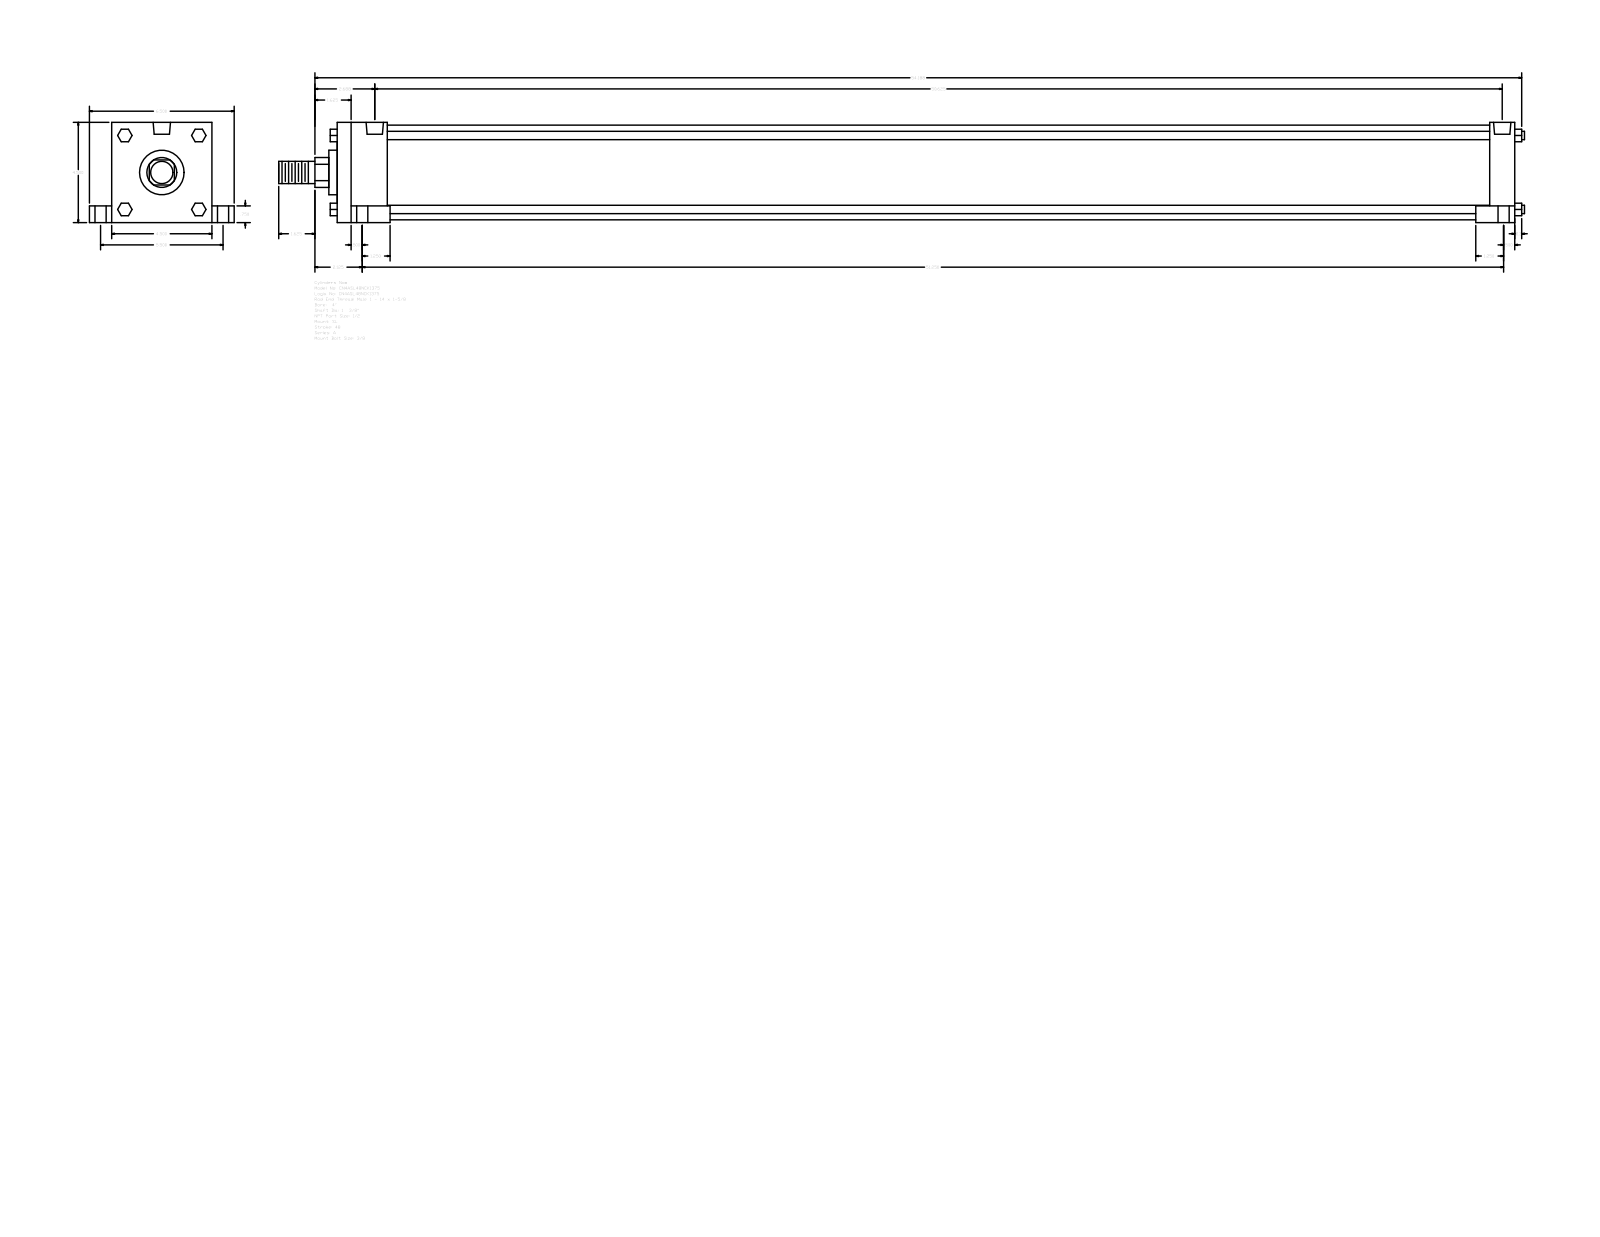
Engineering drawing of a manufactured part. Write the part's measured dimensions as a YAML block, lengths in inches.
part_name: "A_SL__0400_1.375"
step_written_by: "GSSL Pune (CONFIG_CONTROL_DESIGN)"
units: inches
bodies: {solids: 0, faces: 150, planar: 114, cylindrical: 36, other: 0}
overall_size: [55.937, 6.5, 4.5]
round_holes:
  - {diameter: 0.344, count: 4}
  - {diameter: 0.5, count: 4}
  - {diameter: 0.75, count: 4}
  - {diameter: 0.778, count: 2}
round_bosses_or_shafts:
  - {diameter: 0.375, count: 4}
  - {diameter: 4.25, count: 1}
  - {diameter: 2, count: 1}
  - {diameter: 1.375, count: 1}
  - {diameter: 1, count: 1}
partial_cylinders:
  - {radius: 0.672, count: 1}
face_to_face_distances: [4.5, 52.875, 2.25, 1.125, 1, 50.625, 51.75, 49.5, 5.5, 0.75]
hole_center_spacings: [0.125, 2.751, 2.756, 2.807, 2.835, 5.5, 50.375, 50.5]
